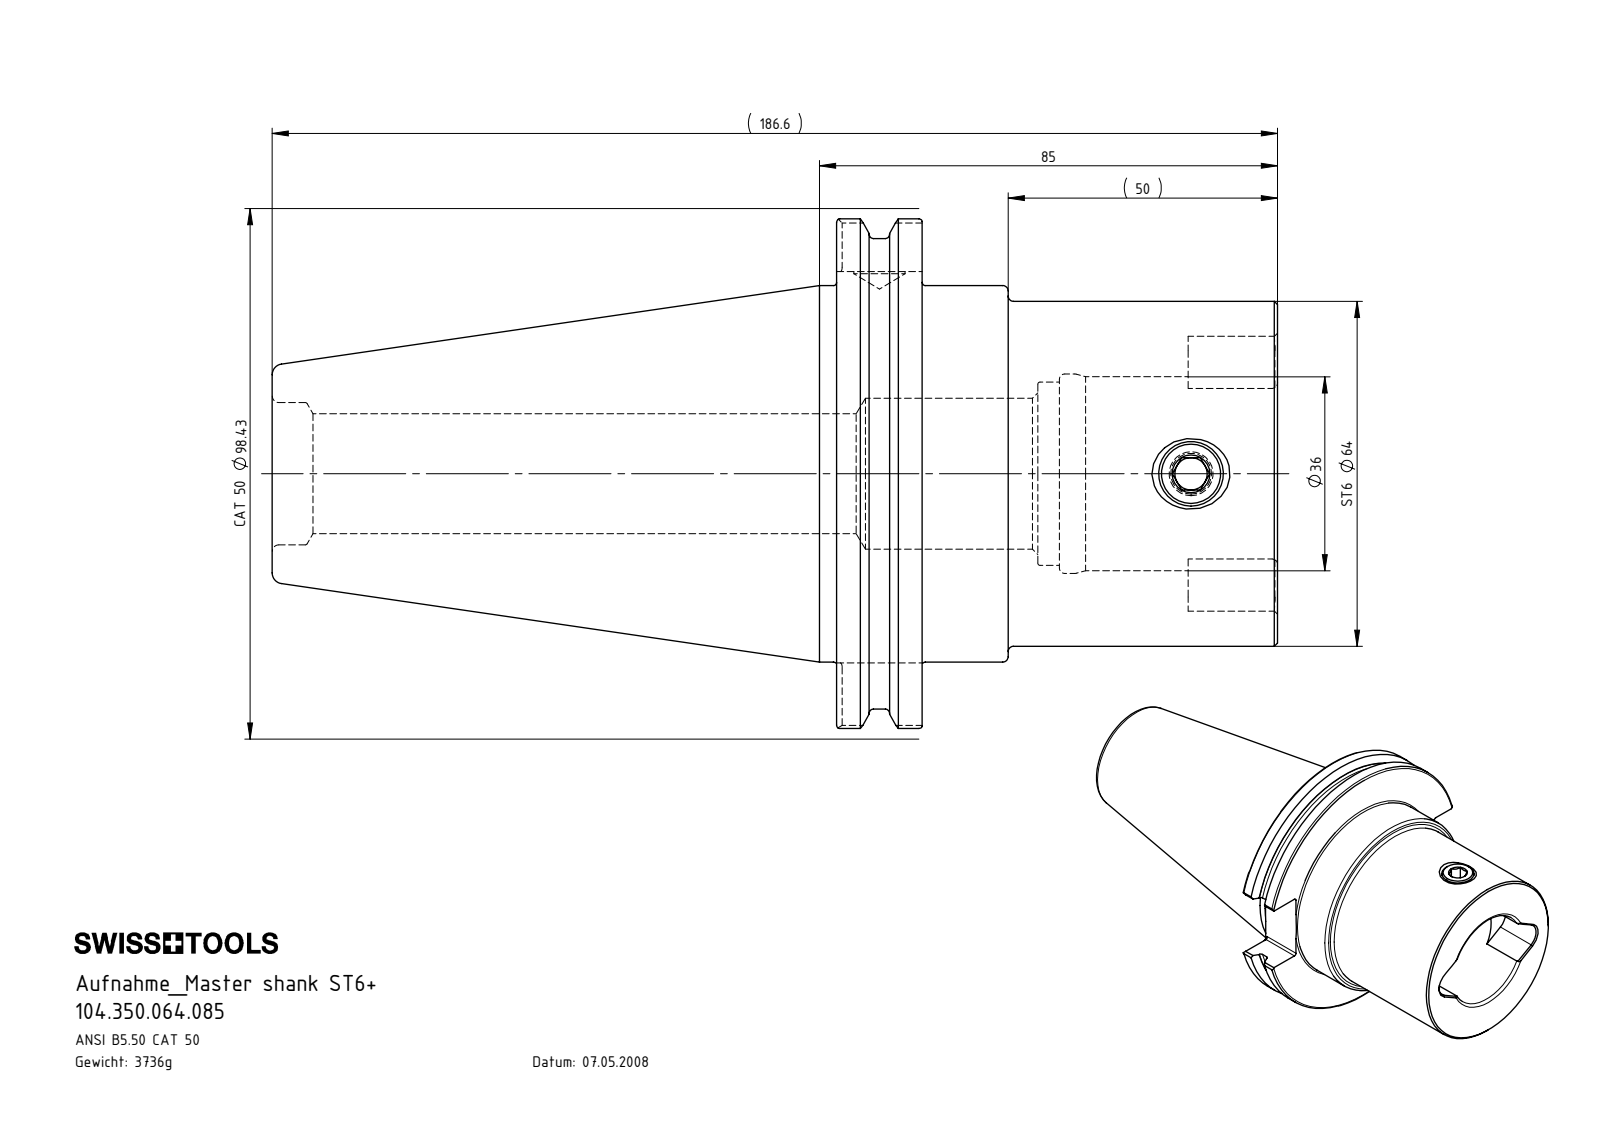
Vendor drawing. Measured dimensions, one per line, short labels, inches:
name: ST6-ER1.001.018_A; CT5.ST6.K01.085; CT5-ST6.K01.085_B
written by: SolidWorks 2017 (AUTOMOTIVE_DESIGN)
unit: in
bodies: 2 solids, 119 faces (51 planar, 29 cylindrical, 39 other)
size: 7.346 × 3.875 × 3.721
volume: 29.04 in³; area: 101.3 in²
holes: 1× ⌀0.236, 1× ⌀0.374, 1× ⌀0.433, 1× ⌀0.876, 1× ⌀1.039, 1× ⌀1.102, 1× ⌀1.339, 1× ⌀1.417, 1× ⌀1.457
bosses: 1× ⌀3.875, 1× ⌀3.583, 1× ⌀2.75, 1× ⌀2.52, 1× ⌀0.472
rounds: 8× R0.031, 2× R0.205
face distances: 0.625, 3.221, 2.596, 4.125, 4.75, 7.346, 2.858, 1.209, 1.012, 5.378
